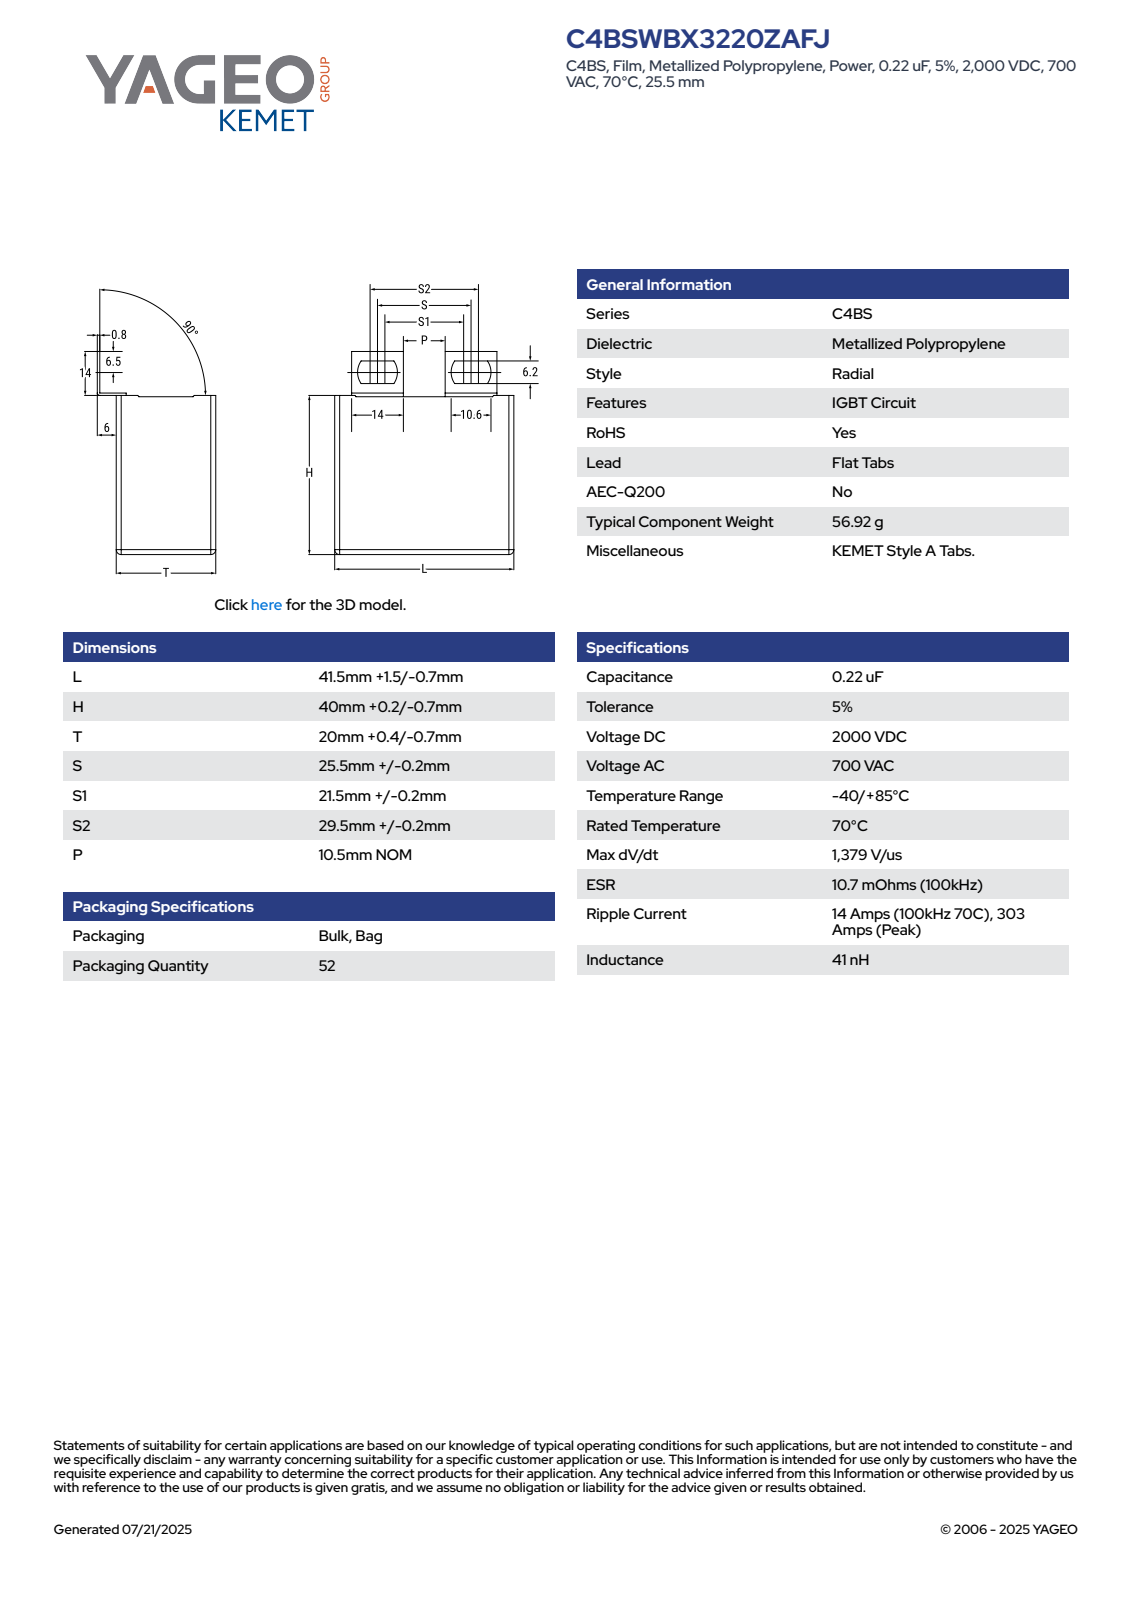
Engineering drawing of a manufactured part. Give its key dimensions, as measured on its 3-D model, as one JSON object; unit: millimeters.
{"part_name": "CFP_C4BA_41.5X40X20_L43H40.2T20.4S25.7", "step_written_by": "SolidWorks 2014 (AUTOMOTIVE_DESIGN)", "units": "millimeters", "bodies": {"solids": 4, "faces": 97, "planar": 91, "cylindrical": 6, "other": 0}, "overall_size": [54.8, 43, 26.41], "volume_mm3": 35659, "surface_area_mm2": 8587, "partial_cylinders_radius": [[6.1, 4]], "face_to_face_distances": [20.4, 43, 40.15, 0.6, 40.2, 40.8, 0.65, 26.4, 6, 25.8]}
